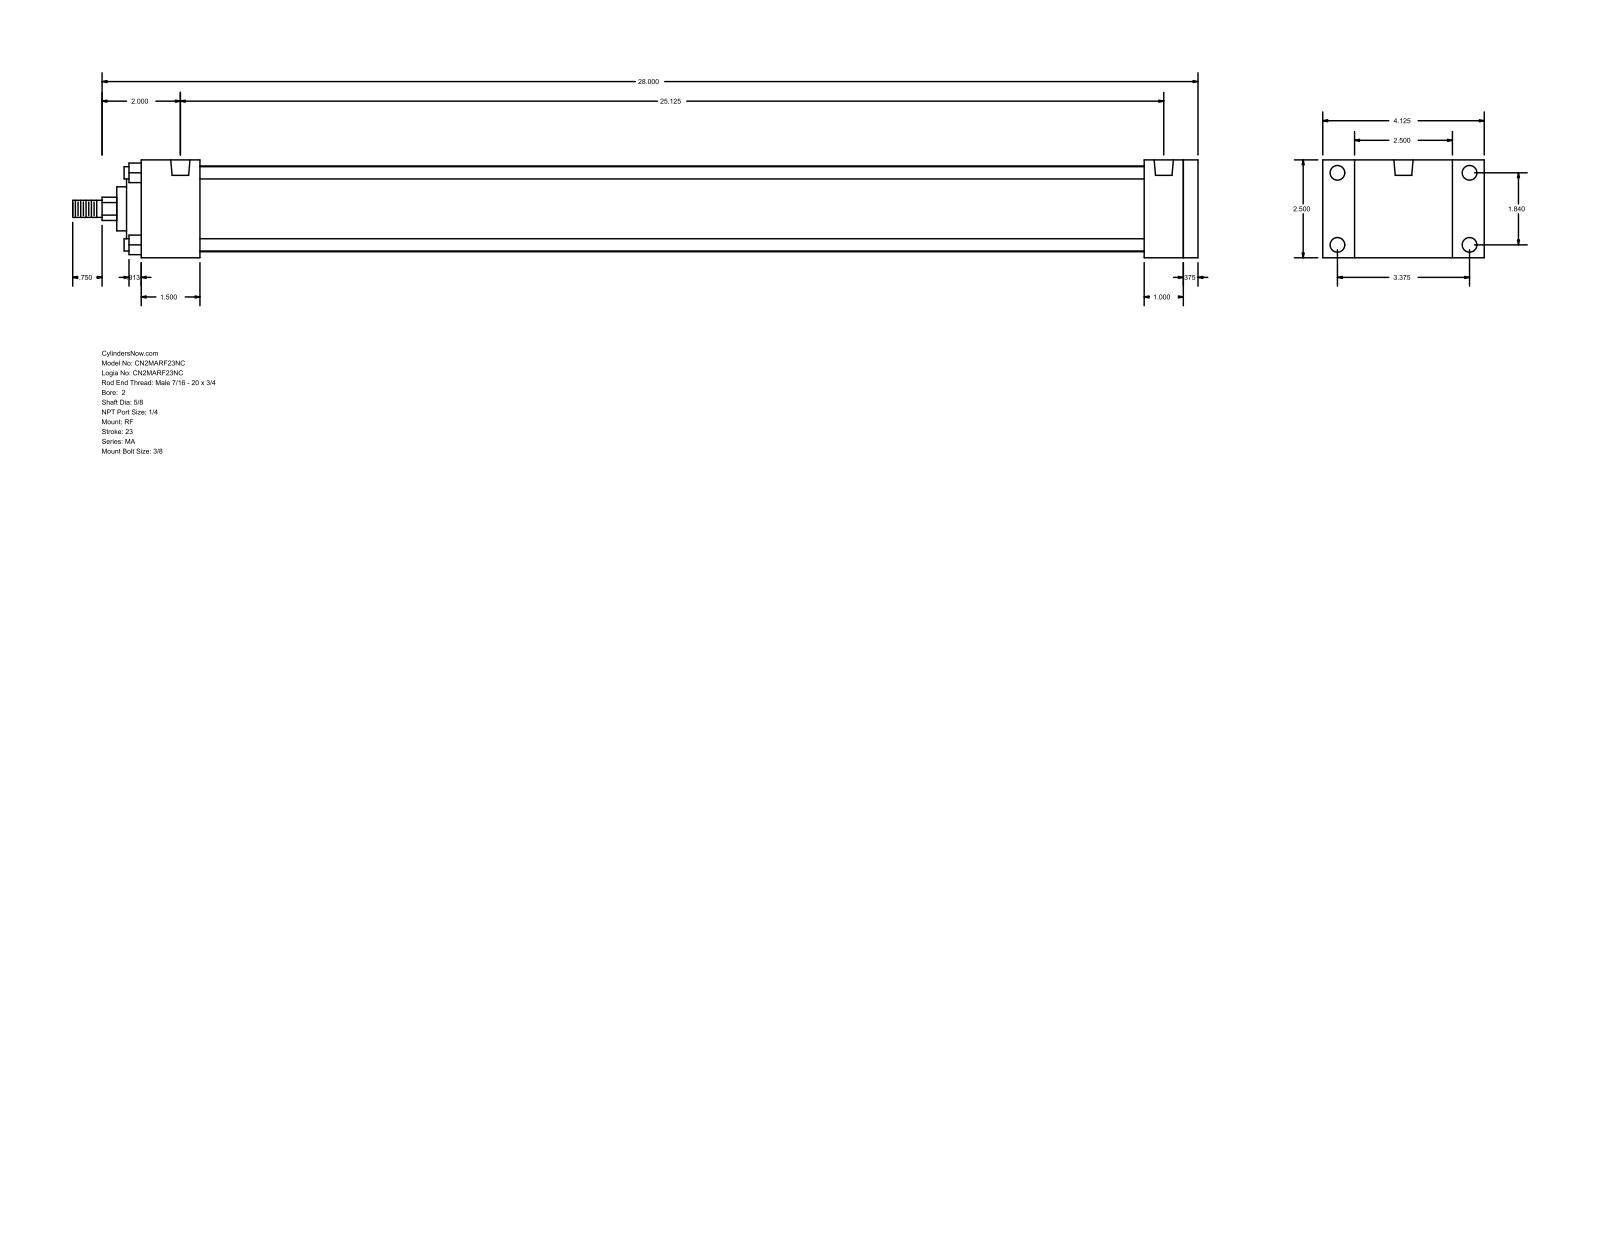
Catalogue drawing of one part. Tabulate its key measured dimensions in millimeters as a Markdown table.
| quantity | value |
| --- | --- |
| part name | MA_RF__0200_0.625 |
| STEP written by | GSSL Pune (CONFIG_CONTROL_DESIGN) |
| units | millimeters |
| bodies | 0 solids, 94 faces (65 planar, 29 cylindrical, 0 other) |
| overall size | 730.25 × 104.78 × 63.5 |
| round holes (diameter × count) | 7.94 × 4, 9.53 × 4, 12.49 × 2 |
| round bosses / shafts (diameter × count) | 7.94 × 4, 55.63 × 1, 50.8 × 1, 28.57 × 1, 15.88 × 1, 11.11 × 1 |
| partial cylindrical surfaces (radius × count) | 7.54 × 1 |
| main face-to-face distances | 63.5, 9.53, 25.4, 38.1, 695.32, 676.27, 34.93, 685.8, 638.17, 647.7 |
| hole center spacings | 46.74, 85.72, 97.63, 638.18 |
